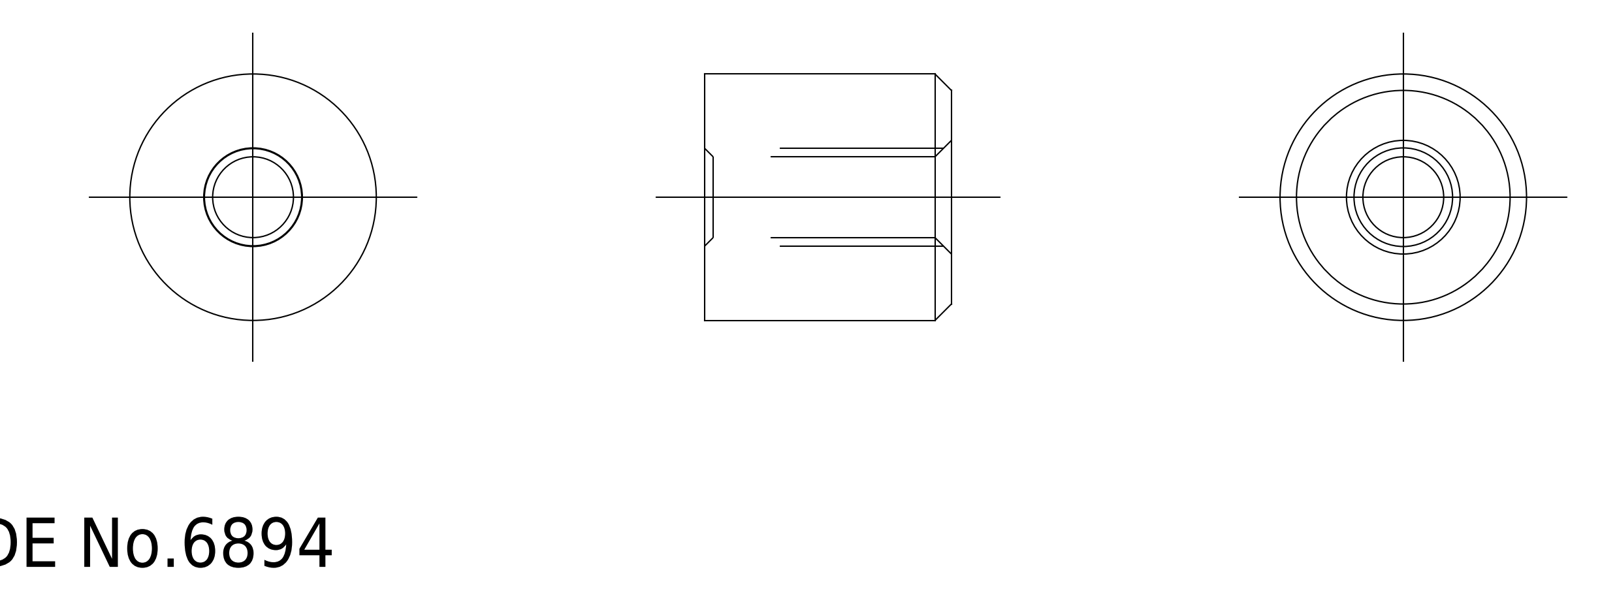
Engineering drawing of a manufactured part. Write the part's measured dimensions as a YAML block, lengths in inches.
part_name: "boss"
step_written_by: "CADfix (AUTOMOTIVE_DESIGN)"
units: inches
bodies: {solids: 1, faces: 10, planar: 0, cylindrical: 0, other: 10}
overall_size: [0.591, 0.591, 0.591]
volume: 0.135
surface_area: 1.942
